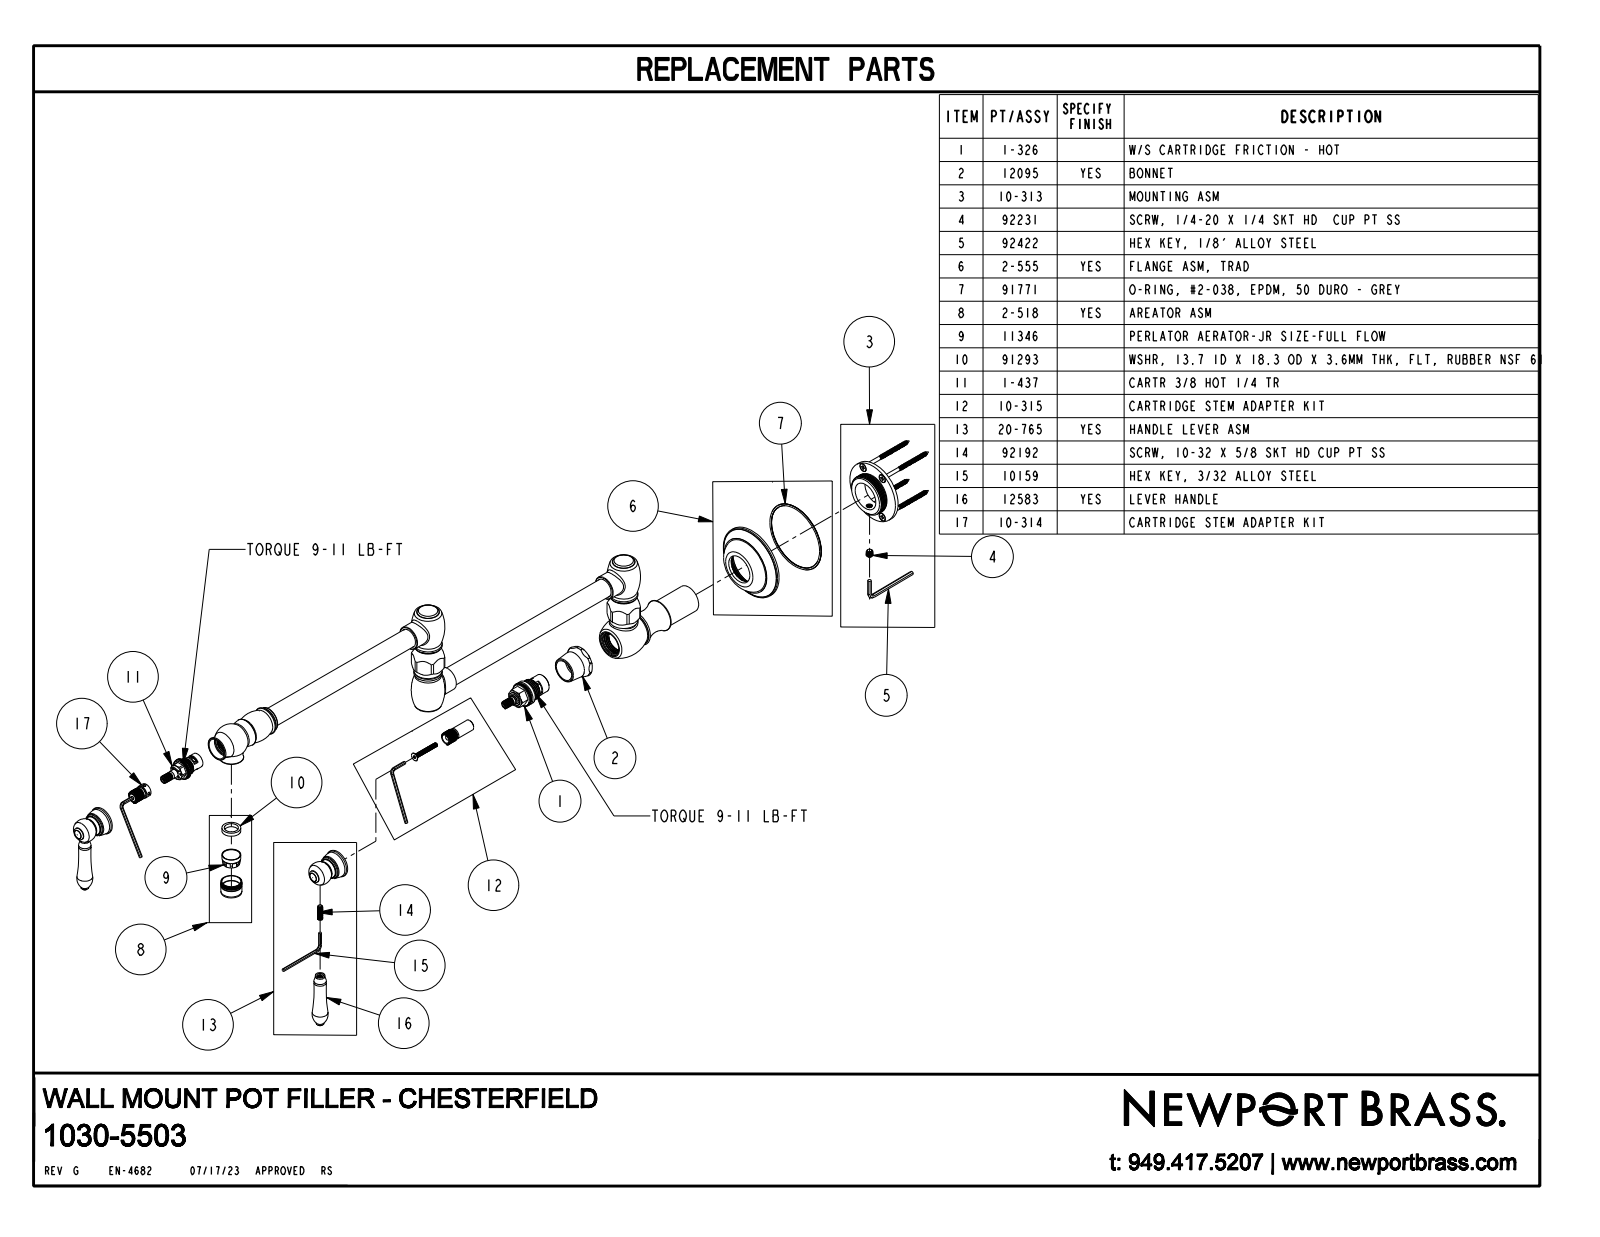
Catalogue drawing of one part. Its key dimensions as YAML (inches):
part_name: "1030-5503"
step_written_by: "CREO PARAMETRIC BY PTC INC, 2018400 (CONFIG_CONTROL_DESIGN)"
units: inches
bodies: {solids: 1, faces: 326, planar: 61, cylindrical: 66, other: 199}
overall_size: [26.879, 9.251, 2.92]
volume: 29.47
surface_area: 134.2
round_bosses_or_shafts:
  - {diameter: 0.94, count: 4}
  - {diameter: 0.48, count: 4}
  - {diameter: 0.75, count: 2}
  - {diameter: 0.36, count: 2}
  - {diameter: 0.3, count: 2}
  - {diameter: 2.92, count: 1}
  - {diameter: 2.29, count: 1}
  - {diameter: 1.082, count: 1}
partial_cylinders:
  - {radius: 0.65, count: 2}
  - {radius: 0.322, count: 1}
  - {radius: 0.505, count: 1}
face_to_face_distances: [1.17, 0.02, 20.285, 0.69, 5.225, 4.535, 1.17, 9.152, 10.322, 7.982]
